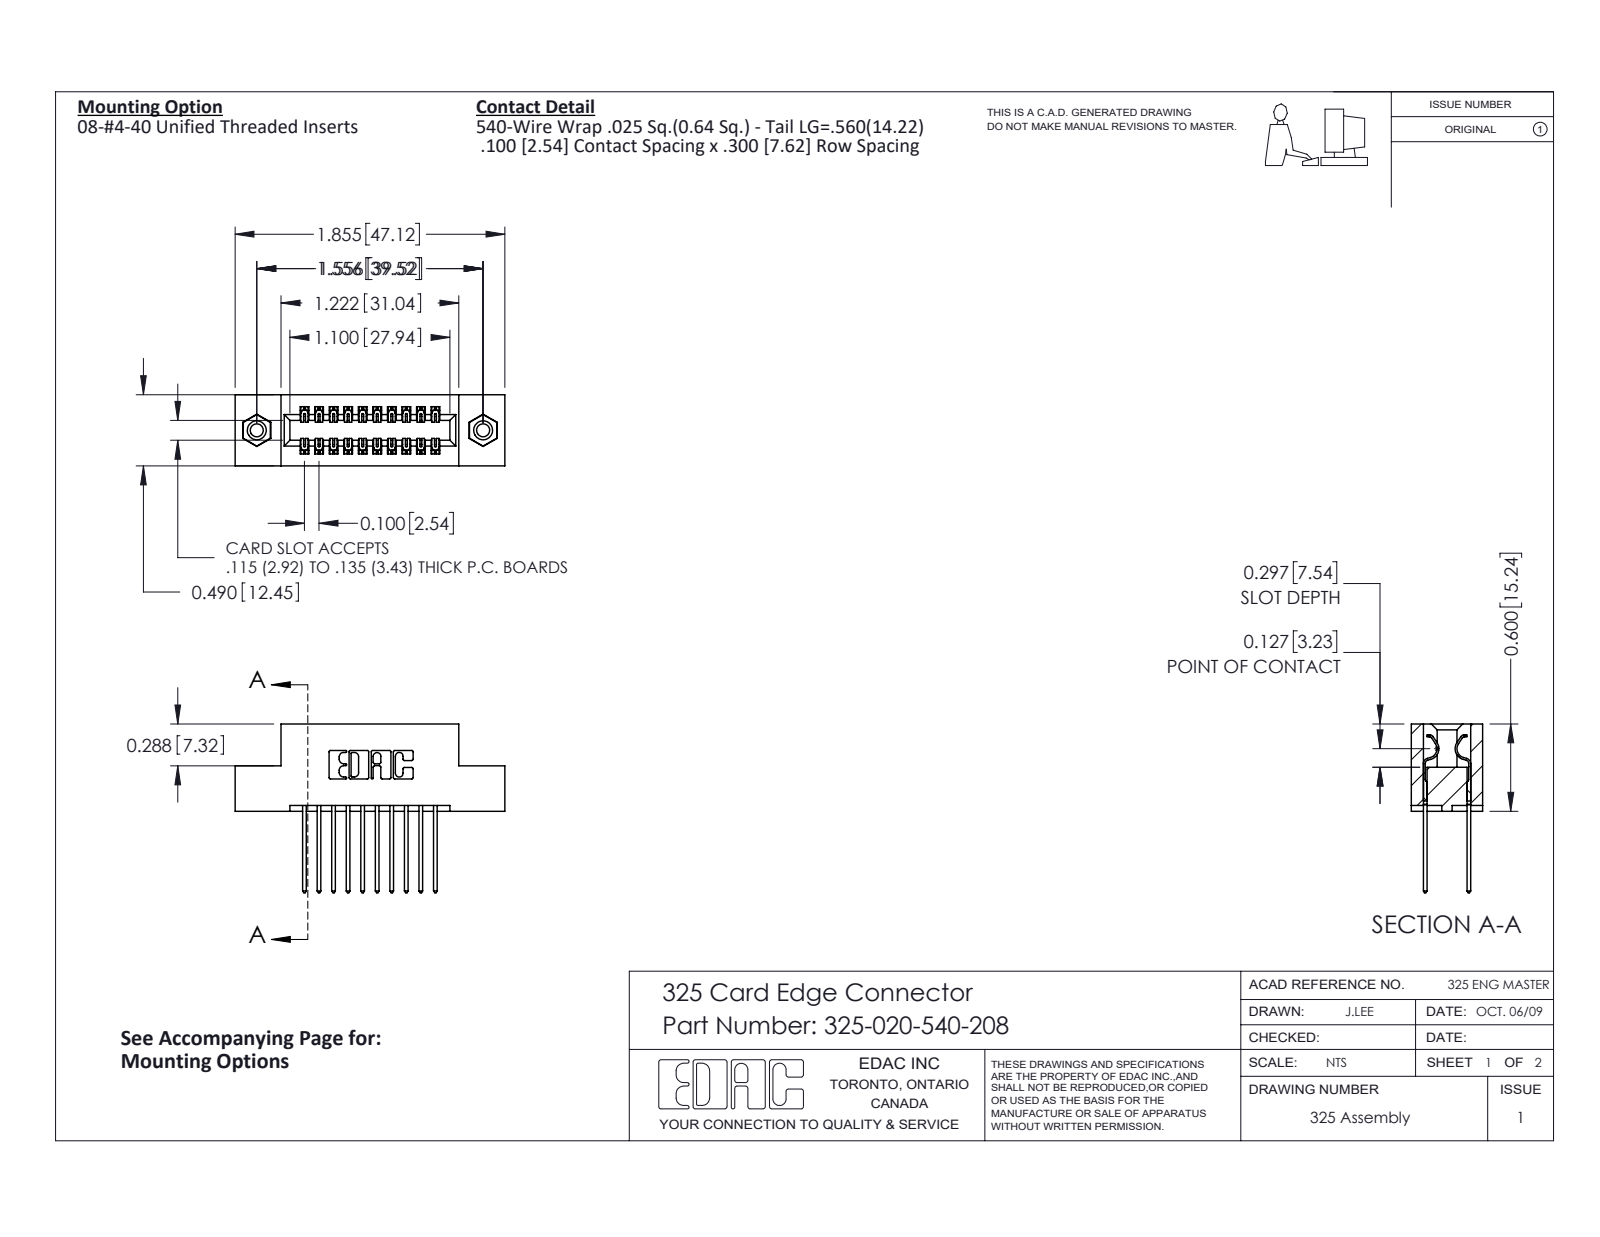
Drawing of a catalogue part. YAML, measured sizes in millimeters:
part_name: "325-020-540-208; 325 Part_TI; 345-250-001_345-250-003-102; 325-292-001_325-293-140"
step_written_by: "SolidWorks 2016 (CONFIG_CONTROL_DESIGN)"
units: millimeters
bodies: {solids: 23, faces: 1214, planar: 822, cylindrical: 376, other: 16}
overall_size: [47.1, 29.5, 12.4]
volume: 5870
surface_area: 6716
round_holes:
  - {diameter: 2.3, count: 2}
  - {diameter: 3.2, count: 2}
  - {diameter: 4.1, count: 2}
round_bosses_or_shafts:
  - {diameter: 3.9, count: 2}
partial_cylinders:
  - {radius: 0.2, count: 30}
  - {radius: 0.3, count: 22}
  - {radius: 0.3, count: 20}
  - {radius: 0.2, count: 6}
  - {radius: 0.8, count: 6}
  - {radius: 0.7, count: 3}
  - {radius: 0.4, count: 2}
  - {radius: 0.6, count: 2}
face_to_face_distances: [7.6, 2.1, 10.3, 12.4, 1, 2.5, 2.7, 9.7, 0.6, 5.1]
hole_center_spacings: [39.5]
